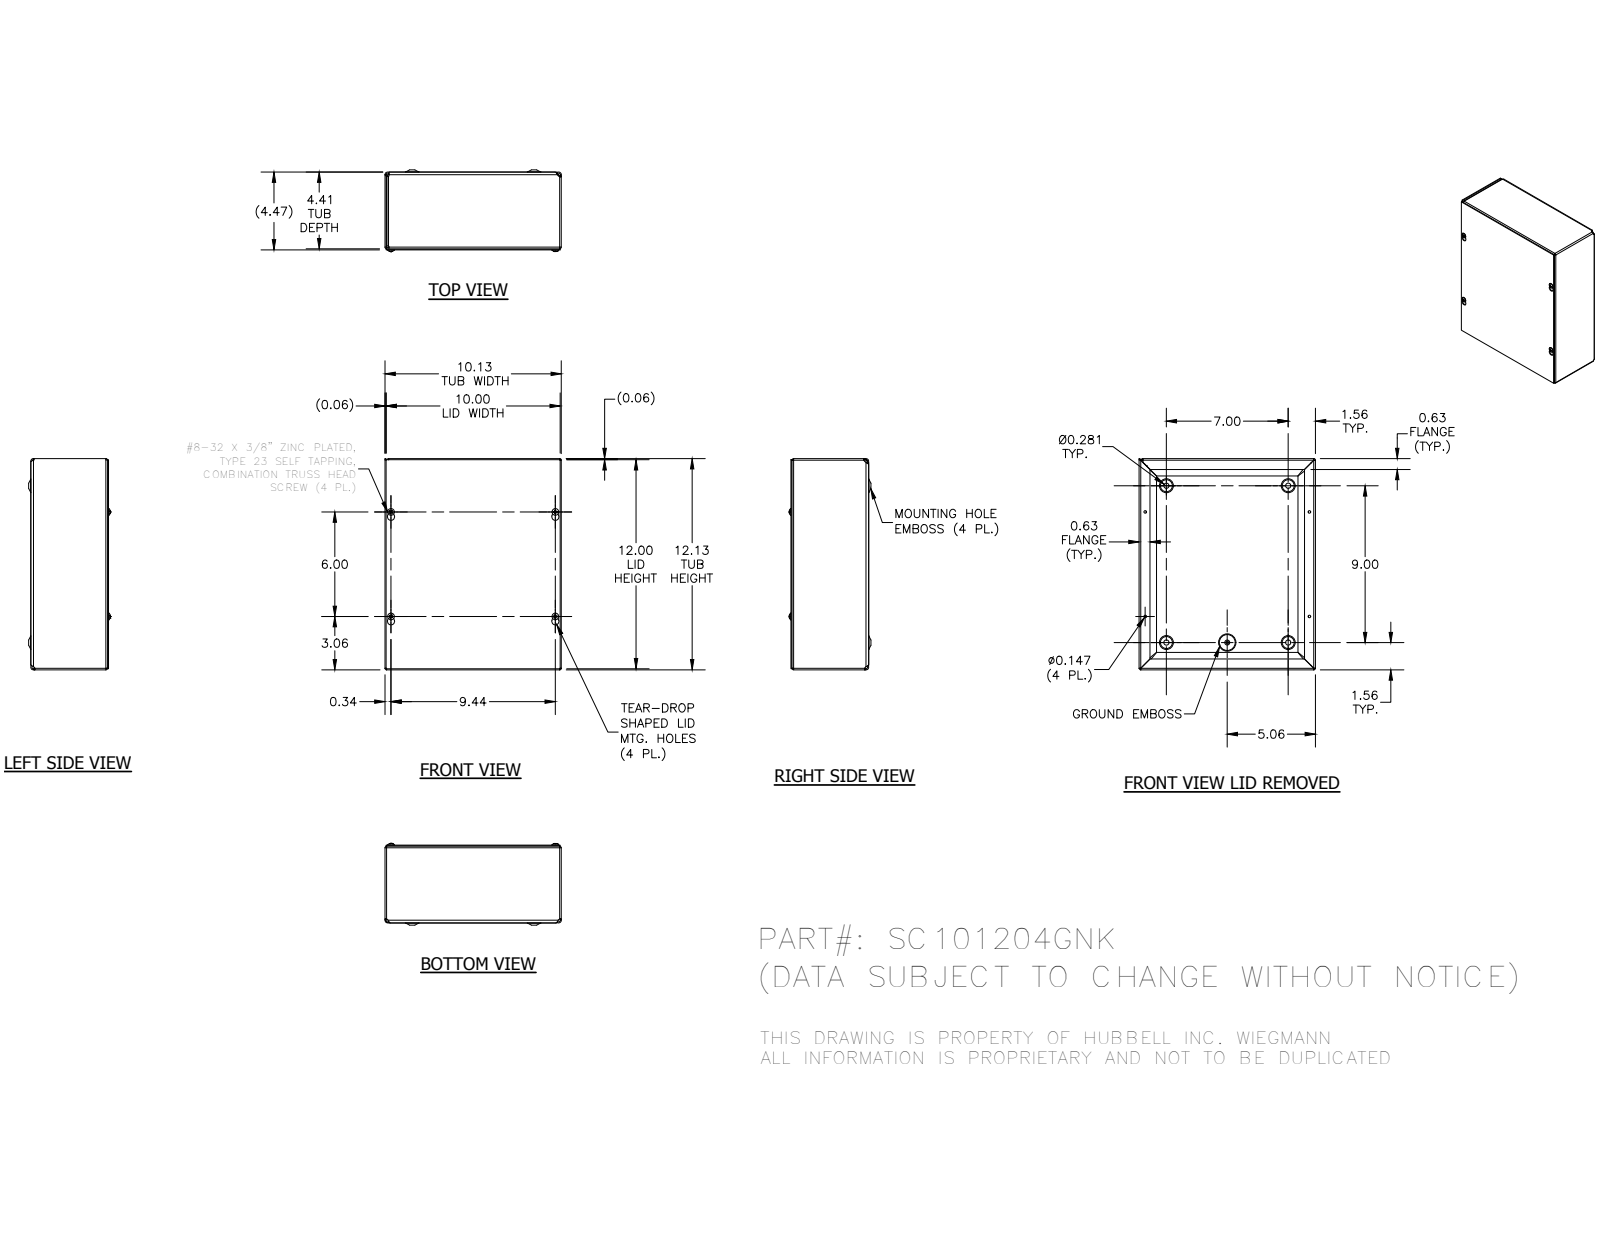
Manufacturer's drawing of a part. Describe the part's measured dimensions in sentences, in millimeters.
The part is named "SC1012GNKBKP; SC101204GNKWRA; SC1012GNKLID; 34056 (+1 more)". Its 3-D file was written by "Autodesk Inventor 2014 (AUTOMOTIVE_DESIGN)". It is 7 solids with 358 faces: 133 planar, 73 cylindrical and 152 other. Overall it measures 307.98 by 257.18 by 119.2 millimeters. Its volume is 495 377 cubic millimeters and its surface area 636 629 square millimeters. Round holes: 4 of diameter 3.73, 4 of diameter 7.62, 1 of diameter 4.19. Round bosses or shafts: 4 of diameter 9.75, 4 of diameter 4.17, 1 of diameter 5.8. Partial cylindrical surfaces (rounded edges, fillets, slot ends): 8 of radius 0.79, 8 of radius 2.37, 4 of radius 1.4, 4 of radius 1.57, 4 of radius 2.38, 4 of radius 2.97, 4 of radius 3.15, 4 of radius 3.17. The main face-to-face distances are 1.57, 110.32, 111.89, 1.59, 111.91, 113.48, 306.4, 1.58, 257.18, 255.61. The hole center spacings are 88.9, 152.4, 177.8, 192.98, 193.02, 212.2, 225.05, 228.6.
